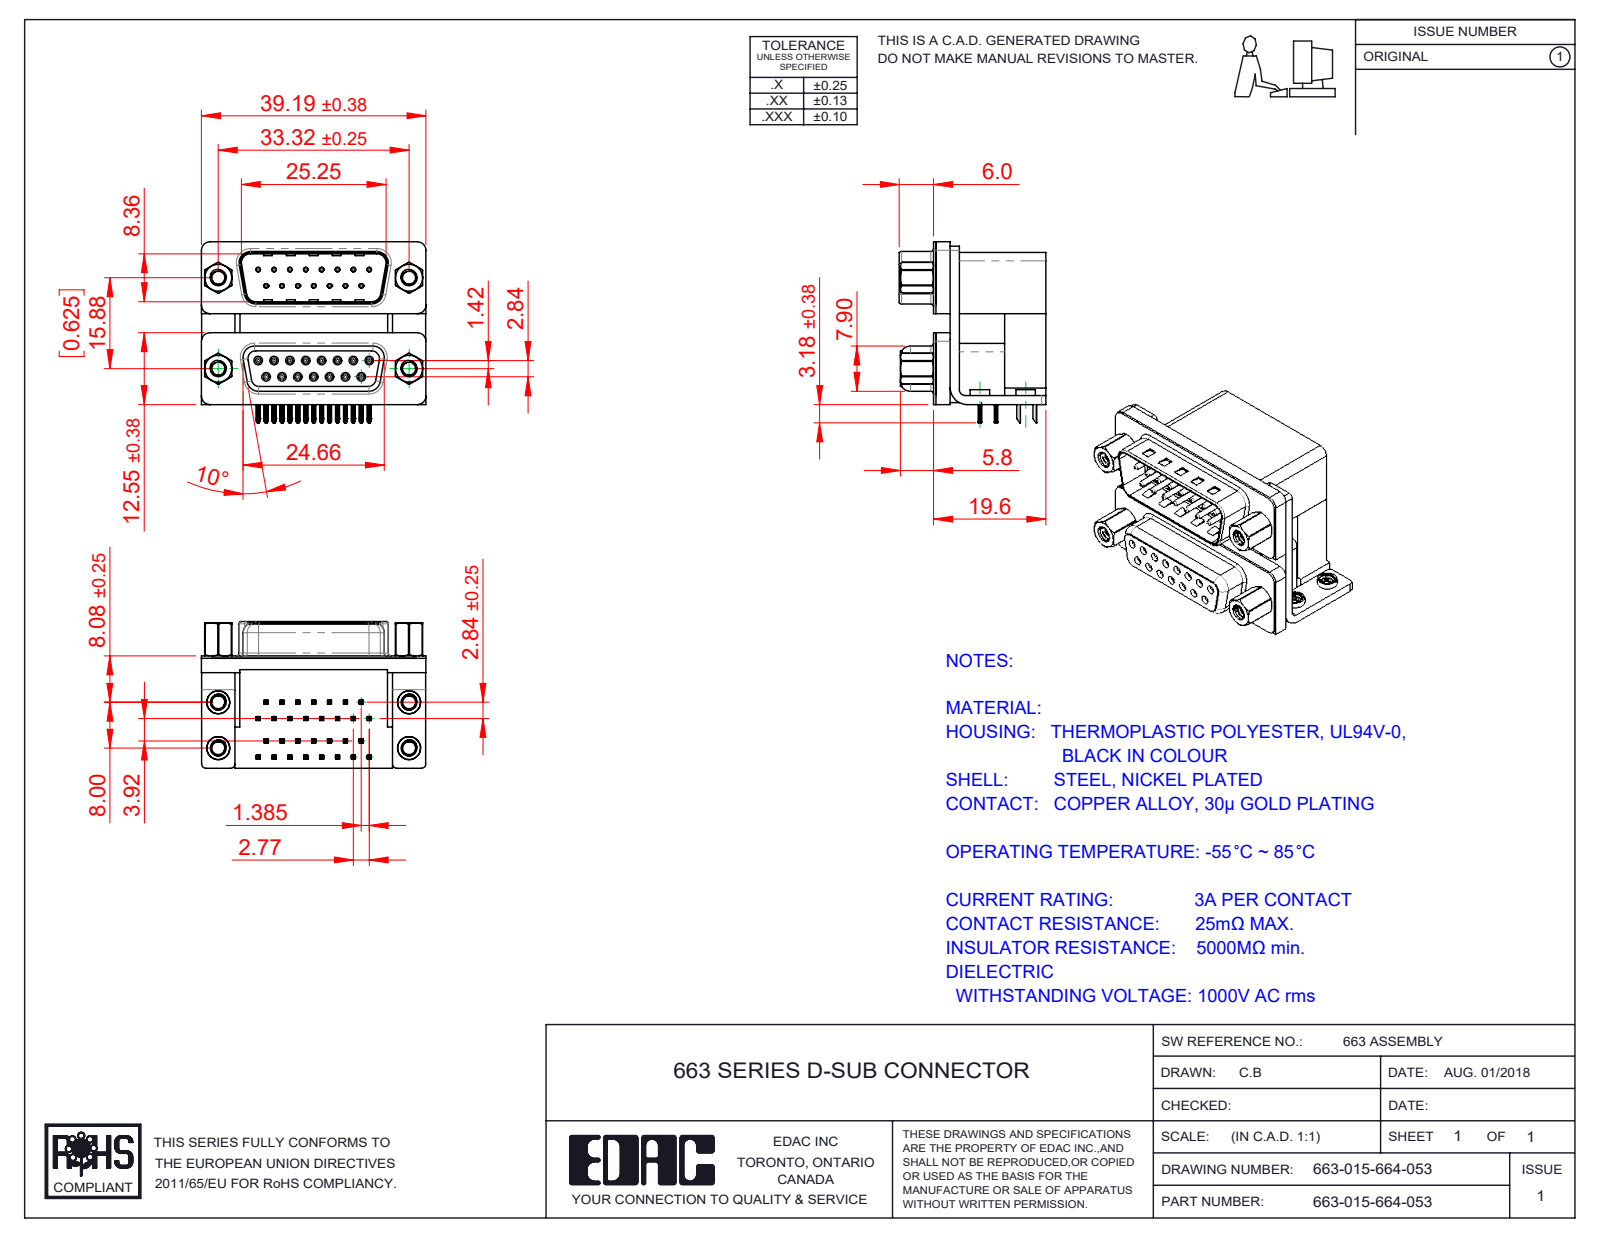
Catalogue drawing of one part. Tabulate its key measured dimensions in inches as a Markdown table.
| quantity | value |
| --- | --- |
| part name | 663 Shell Plug_15 Contacts; 663 Contact Bottom Lower; 663 Housing Upper_15 Contacts L; 663 Threaded Rivet_4-40 (+8 more) |
| STEP written by | SolidWorks 2020 (CONFIG_CONTROL_DESIGN) |
| units | inches |
| bodies | 49 solids, 4304 faces (2071 planar, 1234 cylindrical, 999 other) |
| overall size | 1.543 × 1.244 × 1.008 |
| volume | 0.919 in³ |
| surface area | 26.93 in² |
| round holes (diameter × count) | 0.031 × 30, 0.014 × 15, 0.035 × 15, 0.089 × 8, 0.09 × 4, 0.108 × 4, 0.126 × 4, 0.138 × 4, 0.157 × 4, 0.189 × 4, 0.197 × 4 |
| round bosses / shafts (diameter × count) | 0.047 × 15, 0.03 × 15, 0.193 × 4, 0.187 × 4, 0.157 × 4, 0.154 × 4, 0.134 × 4, 0.11 × 4 |
| partial cylindrical surfaces (radius × count) | 0.004 × 120, 0.006 × 60, 0.01 × 60, 0.005 × 30, 0.014 × 30, 0.059 × 16, 0.013 × 15, 0.02 × 12 |
| main face-to-face distances | 0.016, 0.756, 0.657, 0.098, 0.421, 0.283, 0.472, 0.374, 0.114, 0.772 |
| hole center spacings | 0.124, 0.635, 0.109, 0.662, 0.218, 0.327, 0.625, 0.706 |
